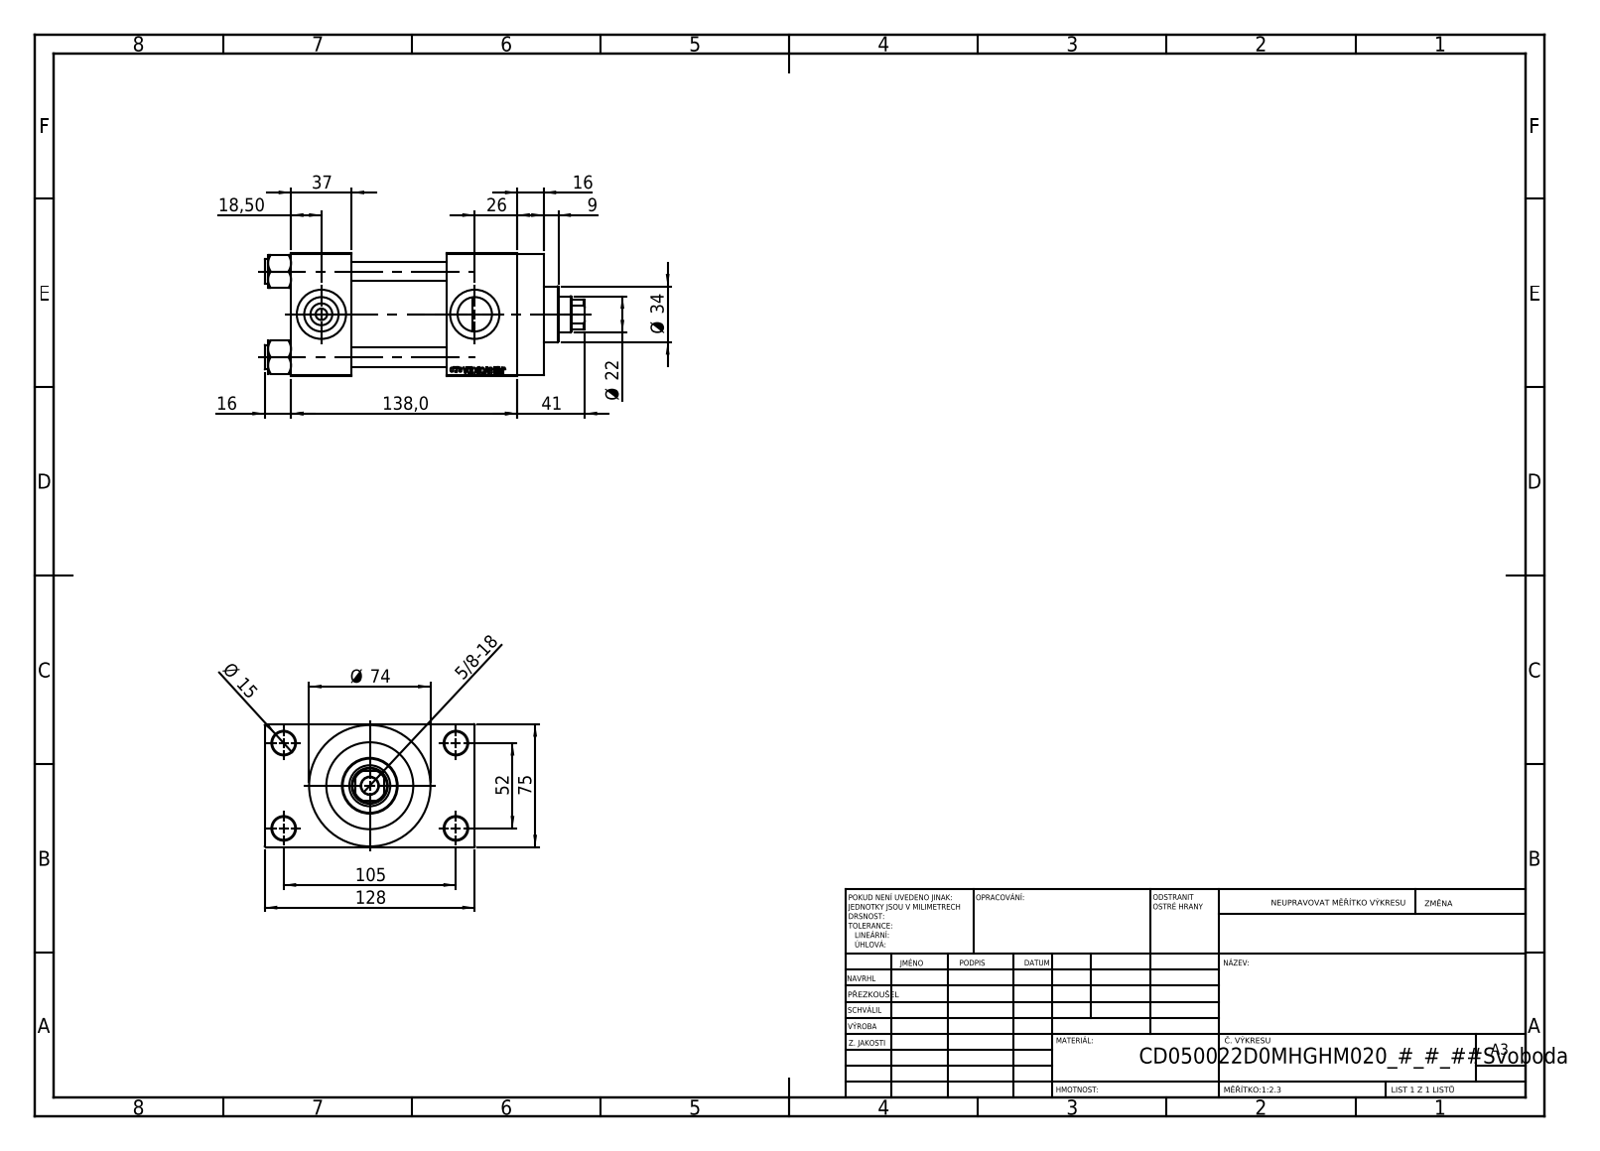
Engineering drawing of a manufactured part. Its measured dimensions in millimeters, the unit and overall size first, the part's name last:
Units: millimetres
Overall size (bounding box): 195 × 128 × 75
Round holes (diameter × count): ⌀12 ×4, ⌀14 ×4, ⌀7 ×2, ⌀20.96 ×2, ⌀30 ×2, ⌀10.5 ×1, ⌀22 ×1, ⌀25 ×1, ⌀41 ×1, ⌀50 ×1, ⌀53 ×1
Round bosses / shafts (diameter × count): ⌀15 ×4, ⌀74 ×1, ⌀56 ×1, ⌀34 ×1
Partial cylindrical surfaces — rounded edges, fillets, slot ends (radius × count): R10.5 ×1
Main face-to-face distances: 75, 58, 37, 95, 26.5, 138, 101, 43, 101.5, 16
Hole centre spacings: 26.35, 36.98, 52.3, 58.43, 58.59, 78.65, 94.37, 52
Volume: 797 518 mm³ · Surface area: 166 687 mm²
Bodies: 11 solids, 1103 faces (497 planar, 88 cylindrical, 518 other)
Part name (STEP PRODUCT): V215CD_VCP_D; V215CD_D_Body; V215CD_NUT_M5_D; V215CD_VC_A (+1 more)
STEP written by: SolidWorks 2019 (CONFIG_CONTROL_DESIGN)
